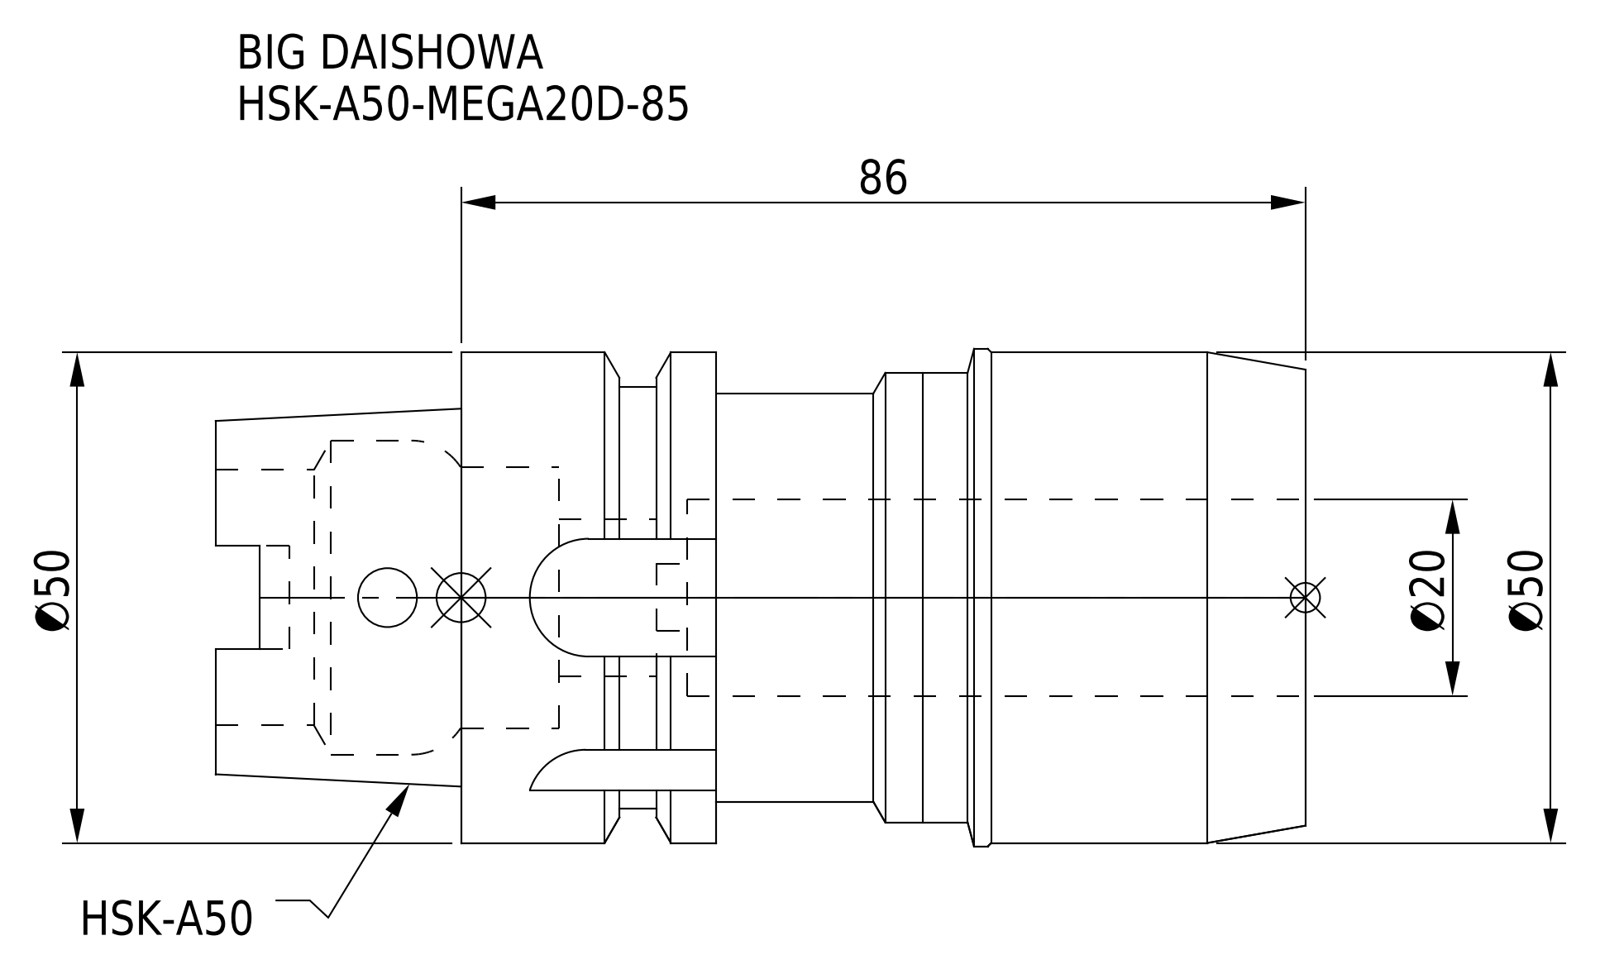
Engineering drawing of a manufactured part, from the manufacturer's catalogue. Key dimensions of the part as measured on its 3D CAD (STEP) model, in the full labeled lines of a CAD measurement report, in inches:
Part name (STEP PRODUCT): HSK-A50-MEGA20D-85
STEP written by: CREO PARAMETRIC BY PTC INC, 2016380 (AUTOMOTIVE_DESIGN)
Units: inches
Bodies: 1 solid, 100 faces (37 planar, 41 cylindrical, 22 other)
Overall size (bounding box): 4.37 × 1.996 × 1.996
Volume: 8.11 in³ · Surface area: 44.46 in²
Round holes (diameter × count): ⌀0.236 ×1, ⌀0.268 ×1, ⌀0.63 ×1, ⌀0.787 ×1, ⌀1.024 ×1, ⌀1.047 ×1, ⌀1.26 ×1
Round bosses / shafts (diameter × count): ⌀1.996 ×1, ⌀1.969 ×1, ⌀1.803 ×1, ⌀1.693 ×1, ⌀1.638 ×1
Partial cylindrical surfaces — rounded edges, fillets, slot ends (radius × count): R0.094 ×4, R0.236 ×4
Main face-to-face distances: 3.386, 2.362, 1.024, 2.994, 0.632, 0.392, 0.118, 4.37, 2.008, 1.376
